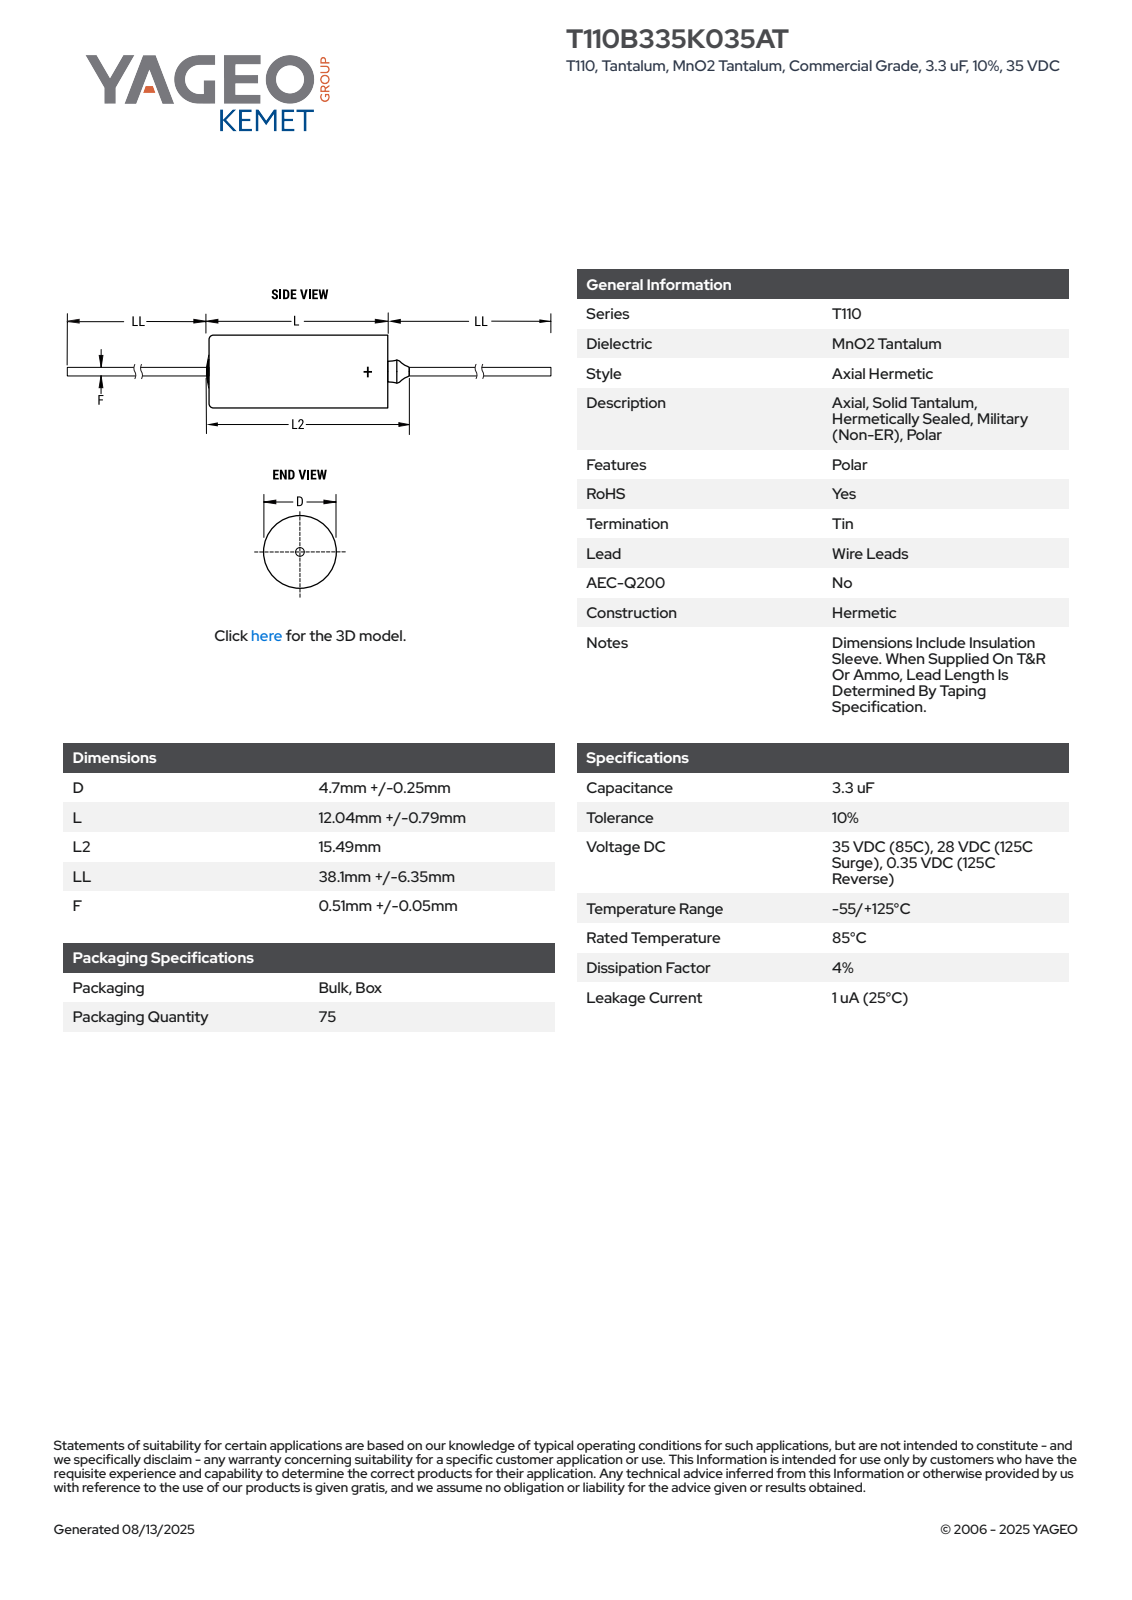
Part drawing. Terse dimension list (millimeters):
name: CTAM_B_D4.95L12.83L215.49LL44.45F0.56
written by: SolidWorks 2014 (AUTOMOTIVE_DESIGN)
unit: mm
bodies: 1 solid, 99 faces (30 planar, 30 cylindrical, 39 other)
size: 101.73 × 4.95 × 4.95
volume: 221 mm³; area: 454 mm²
holes: 1× ⌀4.55
bosses: 1× ⌀4.95, 1× ⌀1.33, 1× ⌀1.3, 1× ⌀0.56
rounds: 1× R2.46
face distances: 9.48, 12.66, 3.18, 44.45, 57.28, 44.62, 54.1, 101.73, 57.11, 47.63
